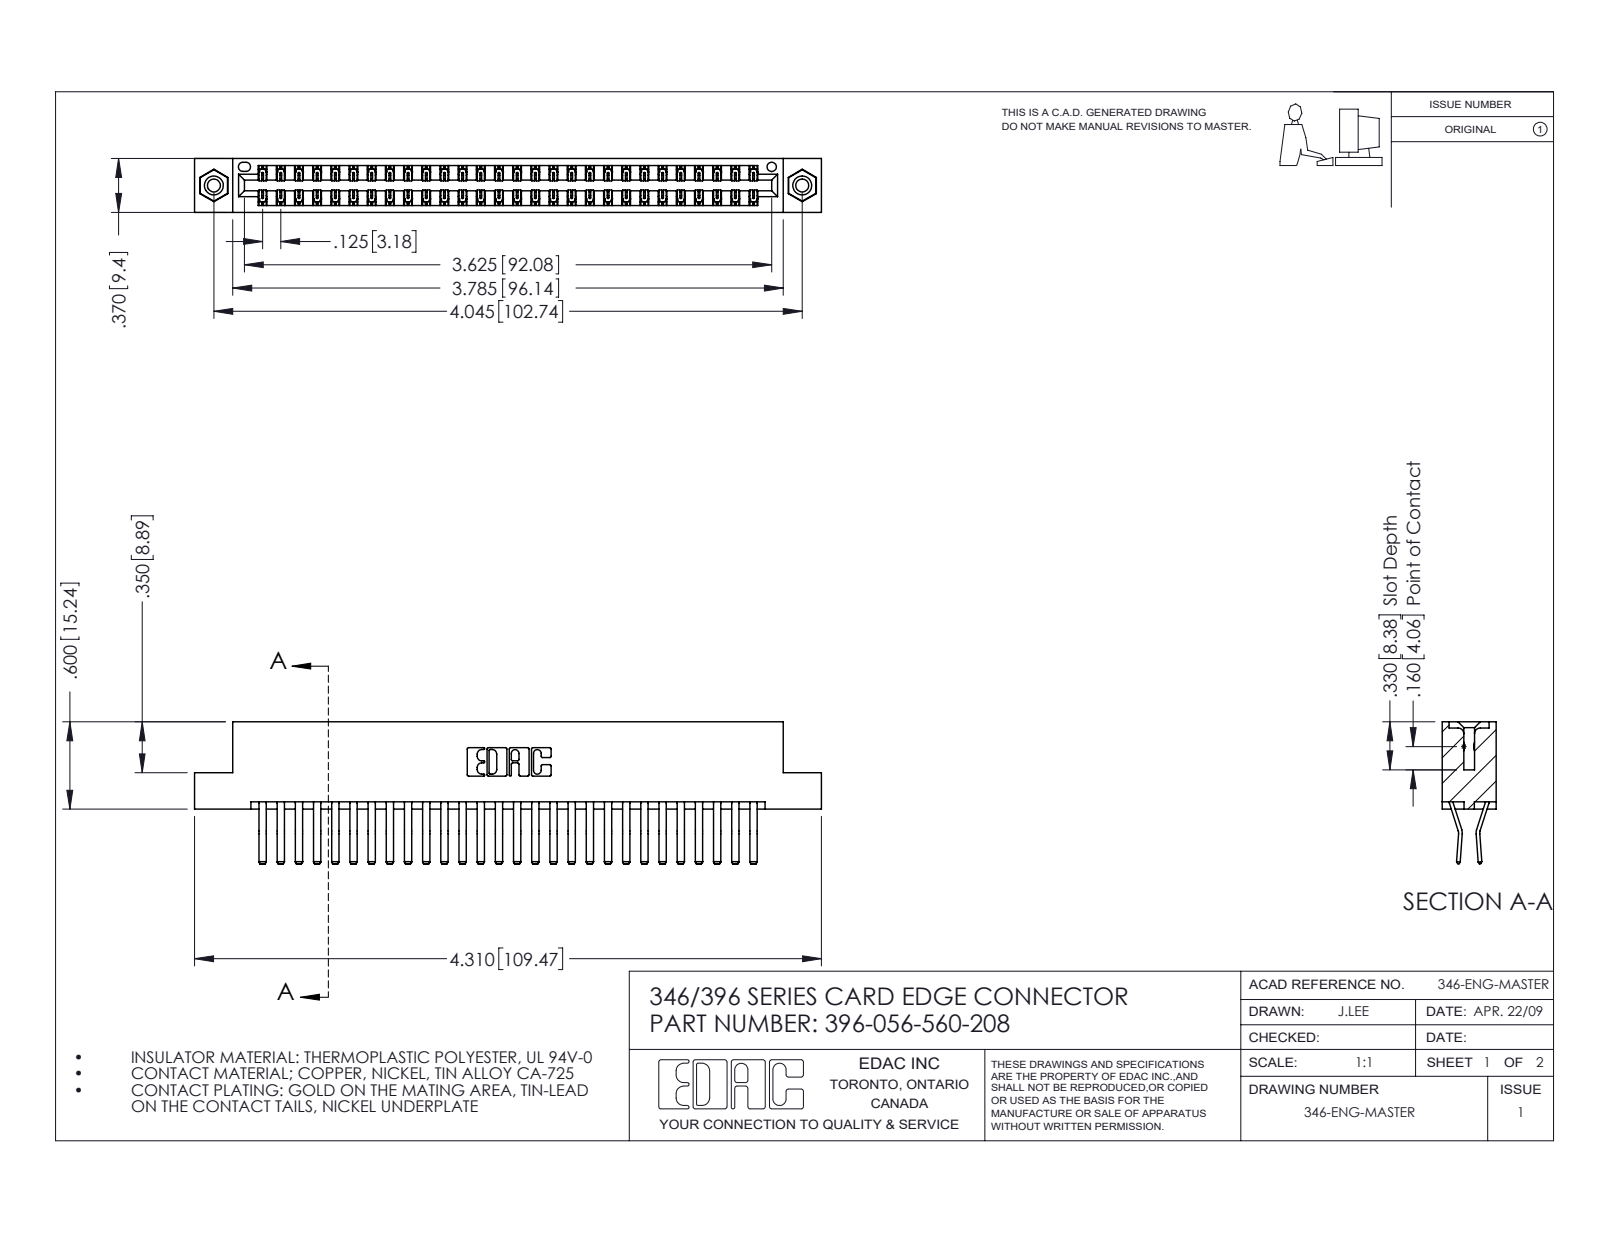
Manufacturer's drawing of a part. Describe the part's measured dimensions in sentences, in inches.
The part is named "396-056-560-208; 345-292-001_560 Tail; 346 Part_Flush Mounting Lugs - 0.156 Dia-TI; 345-250-001_345-250-003-102". Its 3-D file was written by "SolidWorks 2016 (CONFIG_CONTROL_DESIGN)". It is 59 solids with 3206 faces: 2068 planar, 1122 cylindrical and 16 other. Overall it measures 4.31 by 0.975 by 0.37 inches. Its volume is 0.667 cubic inches and its surface area 24.49 square inches. Round holes: 2 of diameter 0.089, 2 of diameter 0.125, 2 of diameter 0.156, 1 of diameter 0.064. Round bosses or shafts: 2 of diameter 0.155. Partial cylindrical surfaces (rounded edges, fillets, slot ends): 84 of radius 0.006, 22 of radius 0.01, 6 of radius 0.007, 6 of radius 0.031, 3 of radius 0.026, 2 of radius 0.01, 2 of radius 0.014, 2 of radius 0.022. The main face-to-face distances are 0.048, 0.322, 0.37, 0.25, 0.025, 0.072, 0.298, 0.275, 0.148, 0.222. The hole center spacings are 0.246, 3.837, 4.045.
